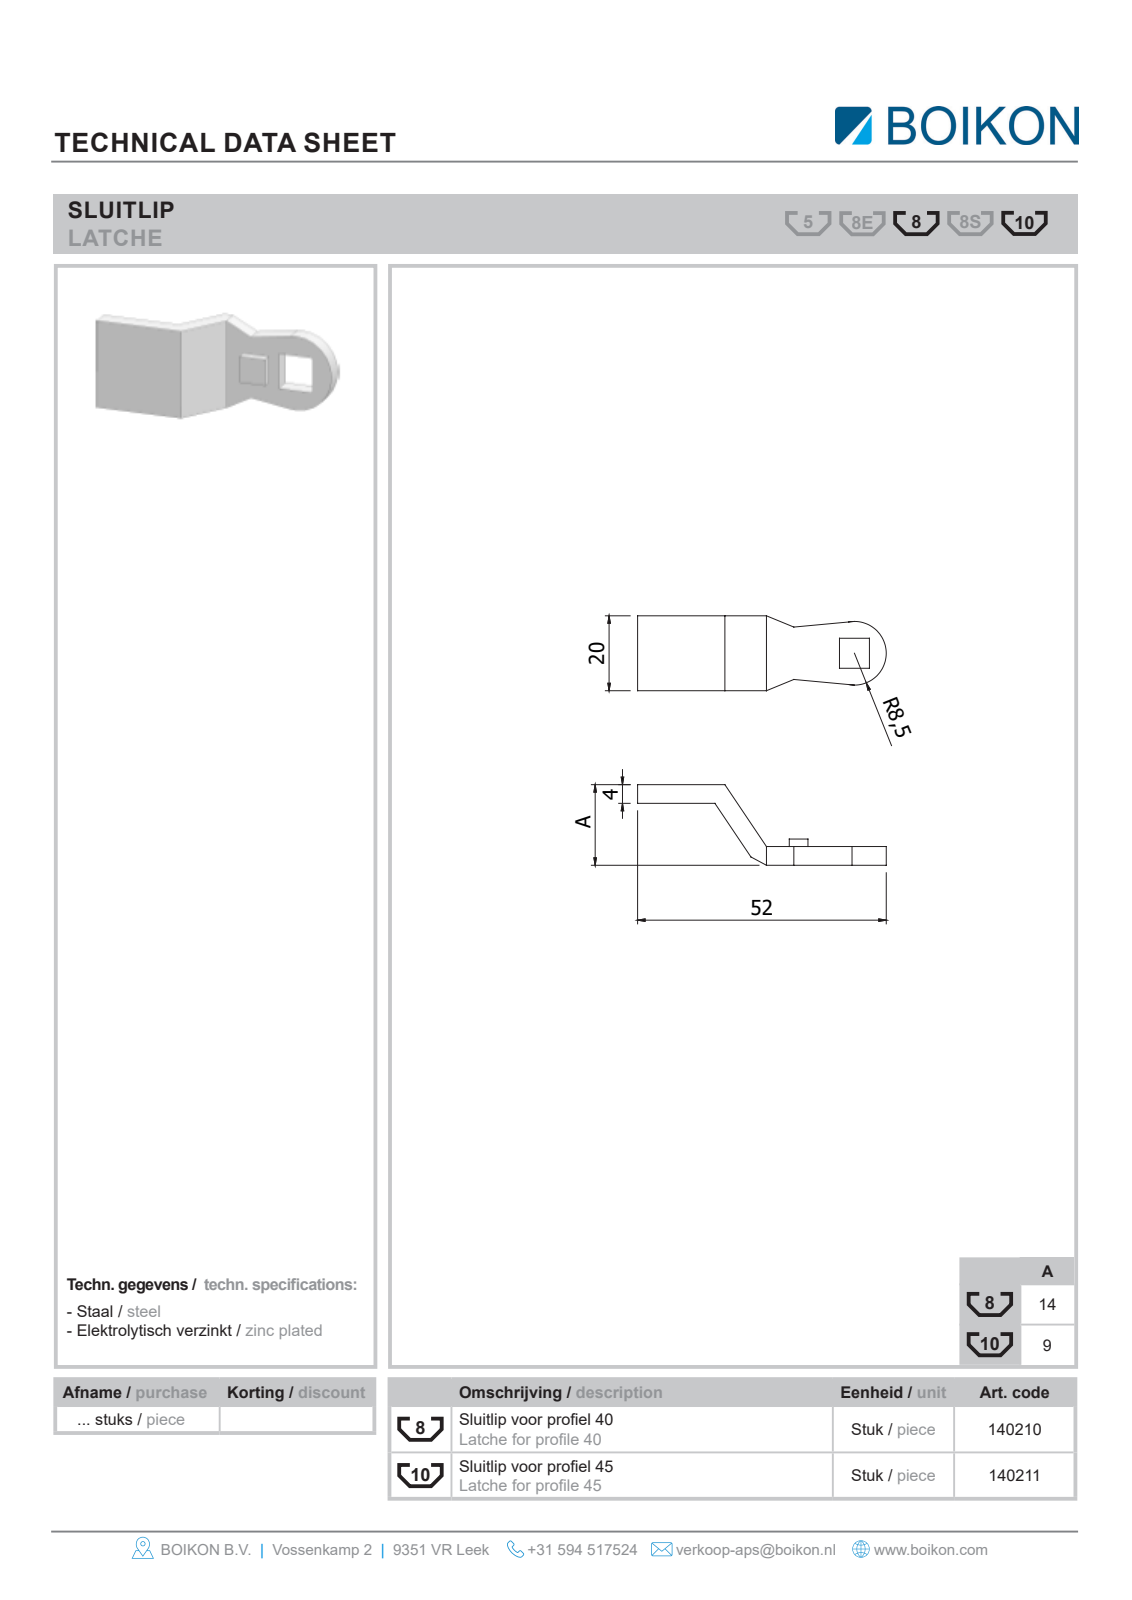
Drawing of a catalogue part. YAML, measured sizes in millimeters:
part_name: "Root; 140210Sluitlip 40 profielBOIKON"
step_written_by: "HiCAD 2013 1802.4 Build 509 (AUTOMOTIVE_DESIGN)"
units: millimeters
bodies: {solids: 1, faces: 23, planar: 22, cylindrical: 1, other: 0}
overall_size: [52, 20, 14]
volume: 3908
surface_area: 2677
partial_cylinders:
  - {radius: 8.5, count: 1}
face_to_face_distances: [4, 10, 14, 6, 3.99, 20, 8, 7, 2, 39.5]
